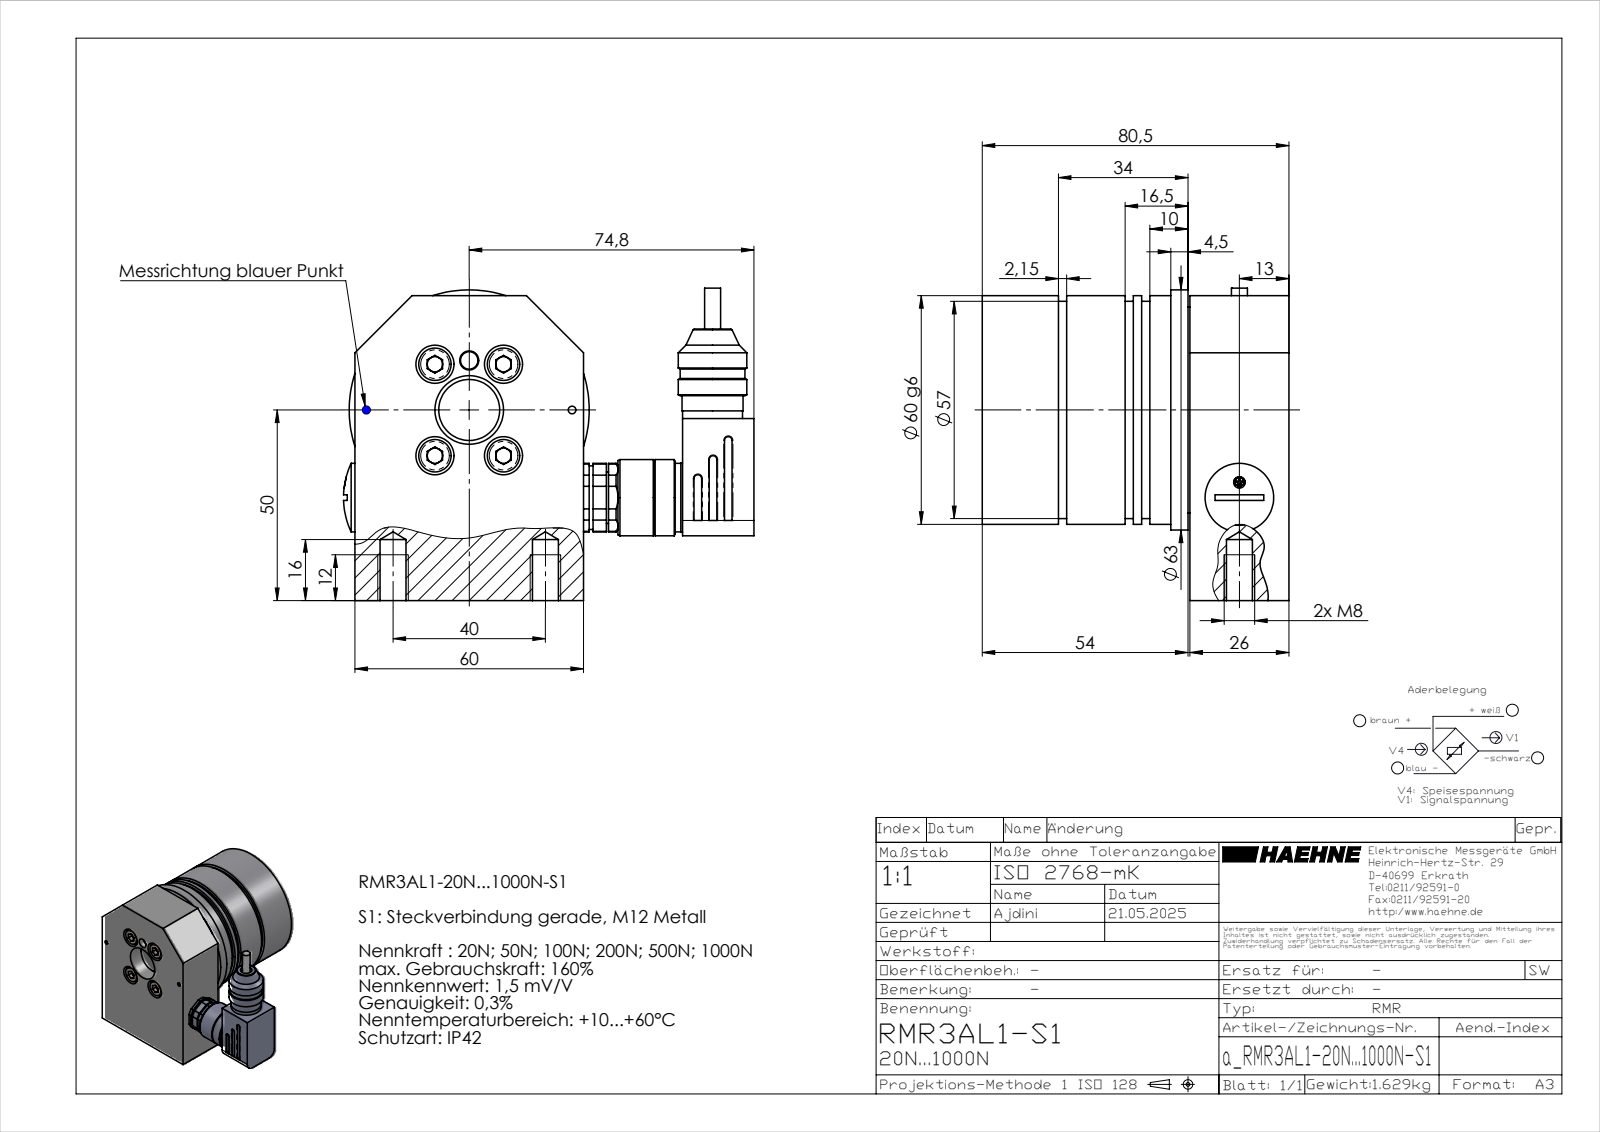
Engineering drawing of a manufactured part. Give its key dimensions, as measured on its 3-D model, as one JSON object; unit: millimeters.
{"part_name": "a_RMR3AL1-20N...1000N-S1", "step_written_by": "SolidWorks 2023 (AUTOMOTIVE_DESIGN)", "units": "millimeters", "bodies": {"solids": 17, "faces": 556, "planar": 279, "cylindrical": 181, "other": 96}, "overall_size": [107.74, 81.98, 80.5], "volume_mm3": 250609, "surface_area_mm2": 77185, "round_holes": [[4.2, 4], [5.3, 4], [10, 4], [2, 2], [6.8, 2], [0.64, 1], [3, 1], [4.5, 1], [5, 1], [6, 1], [8.37, 1], [11.5, 1]], "round_bosses_or_shafts": [[0.86, 5], [8.5, 4], [5, 4], [1.5, 4], [1, 4], [18, 2], [16, 2], [63, 1]], "partial_cylinders_radius": [[0.2, 12], [1, 11], [0.3, 6], [4, 2], [0.57, 1], [0.65, 1], [0.77, 1], [3.5, 1]], "face_to_face_distances": [11.5, 48.5, 37, 26, 73, 54.5, 15, 11, 62, 47], "hole_center_spacings": [15, 21.63, 37.95, 9.06, 18, 24, 26.57, 27]}
